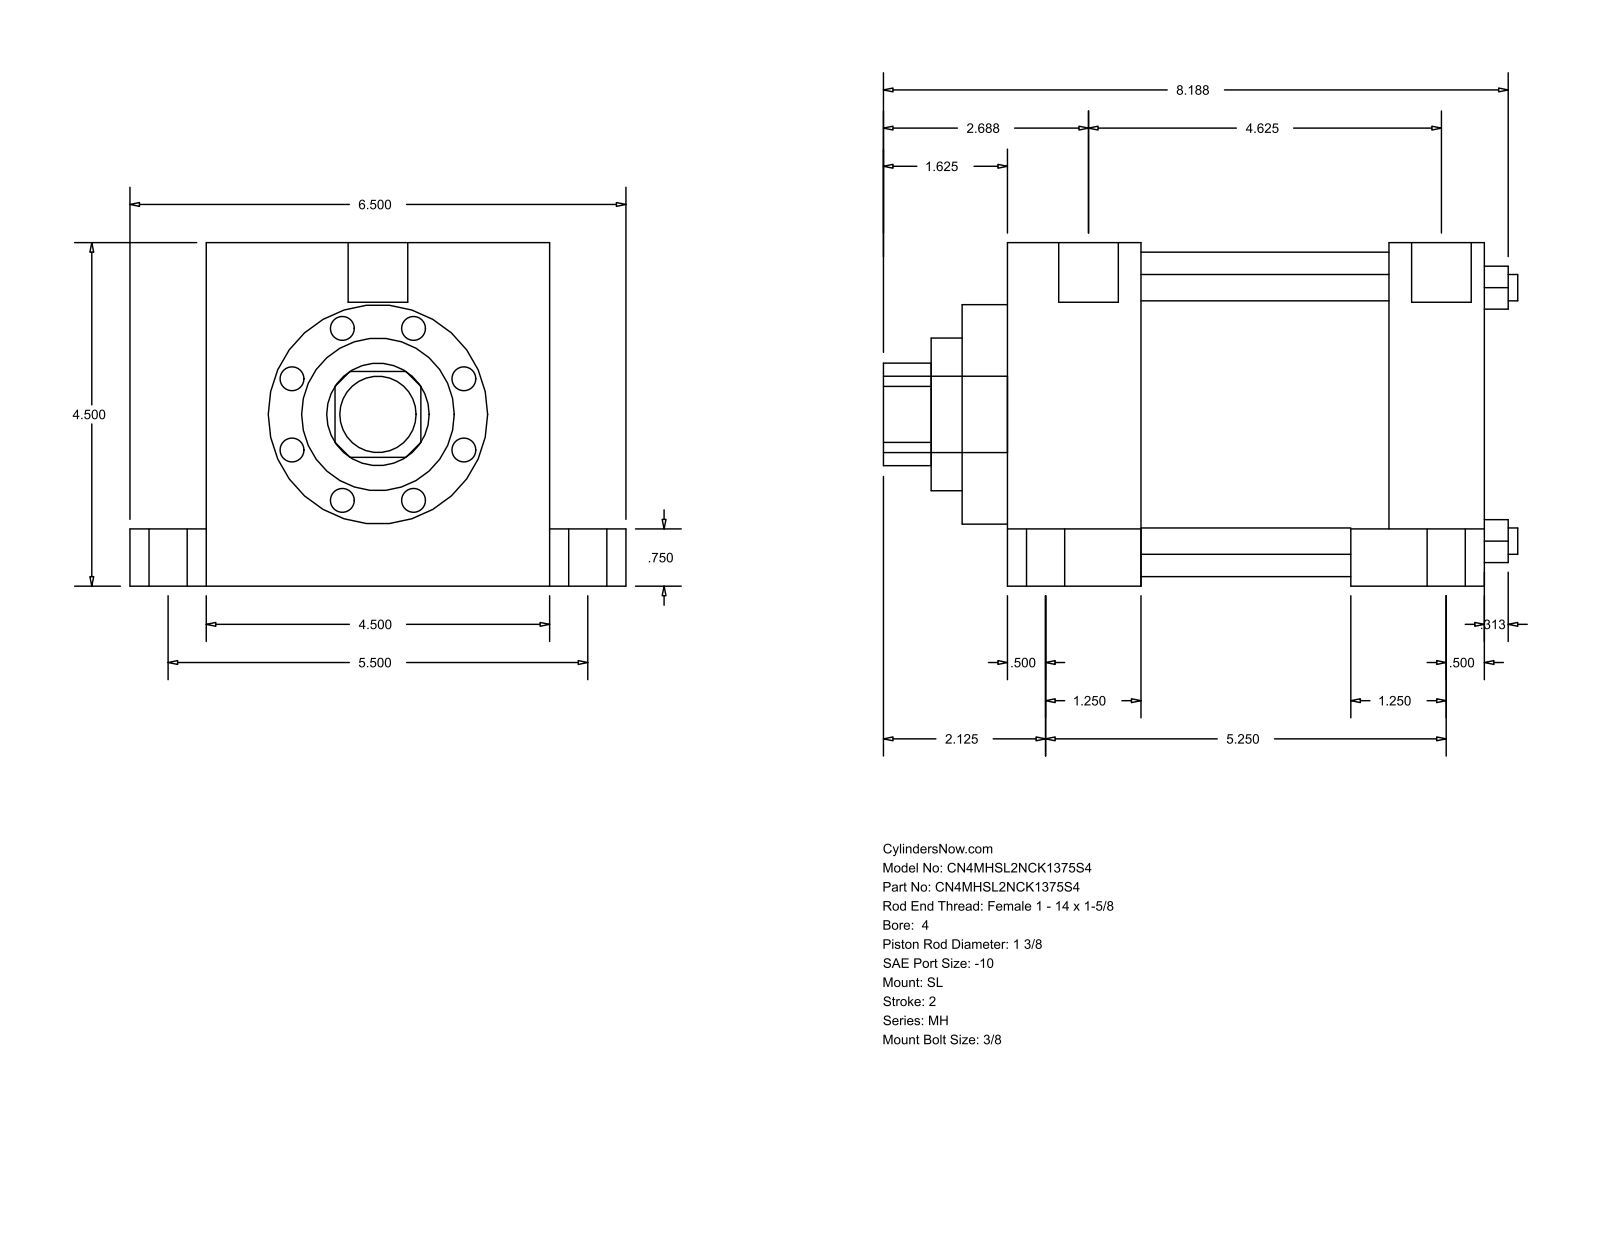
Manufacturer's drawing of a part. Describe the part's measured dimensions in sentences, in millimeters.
The part is named "MH_SL__0400_1.375". Its 3-D file was written by "GSSL Pune (CONFIG_CONTROL_DESIGN)". It is 0 solids with 110 faces: 77 planar, 33 cylindrical and 0 other. Overall it measures 211.14 by 165.1 by 114.3 millimeters. Round holes: 4 of diameter 8.76, 1 of diameter 34.92, 1 of diameter 50.8, 1 of diameter 73.03, 1 of diameter 107.95. Round bosses or shafts: 4 of diameter 19.05, 4 of diameter 12.7, 4 of diameter 8.73, 2 of diameter 19.84, 1 of diameter 25.4. Partial cylindrical surfaces (rounded edges, fillets, slot ends): 1 of radius 17.06. The main face-to-face distances are 114.3, 158.76, 44.45, 114.31, 127.01, 82.56, 31.75, 25.4, 139.7, 19.05. The hole center spacings are 59.62, 84.32, 119.25.
